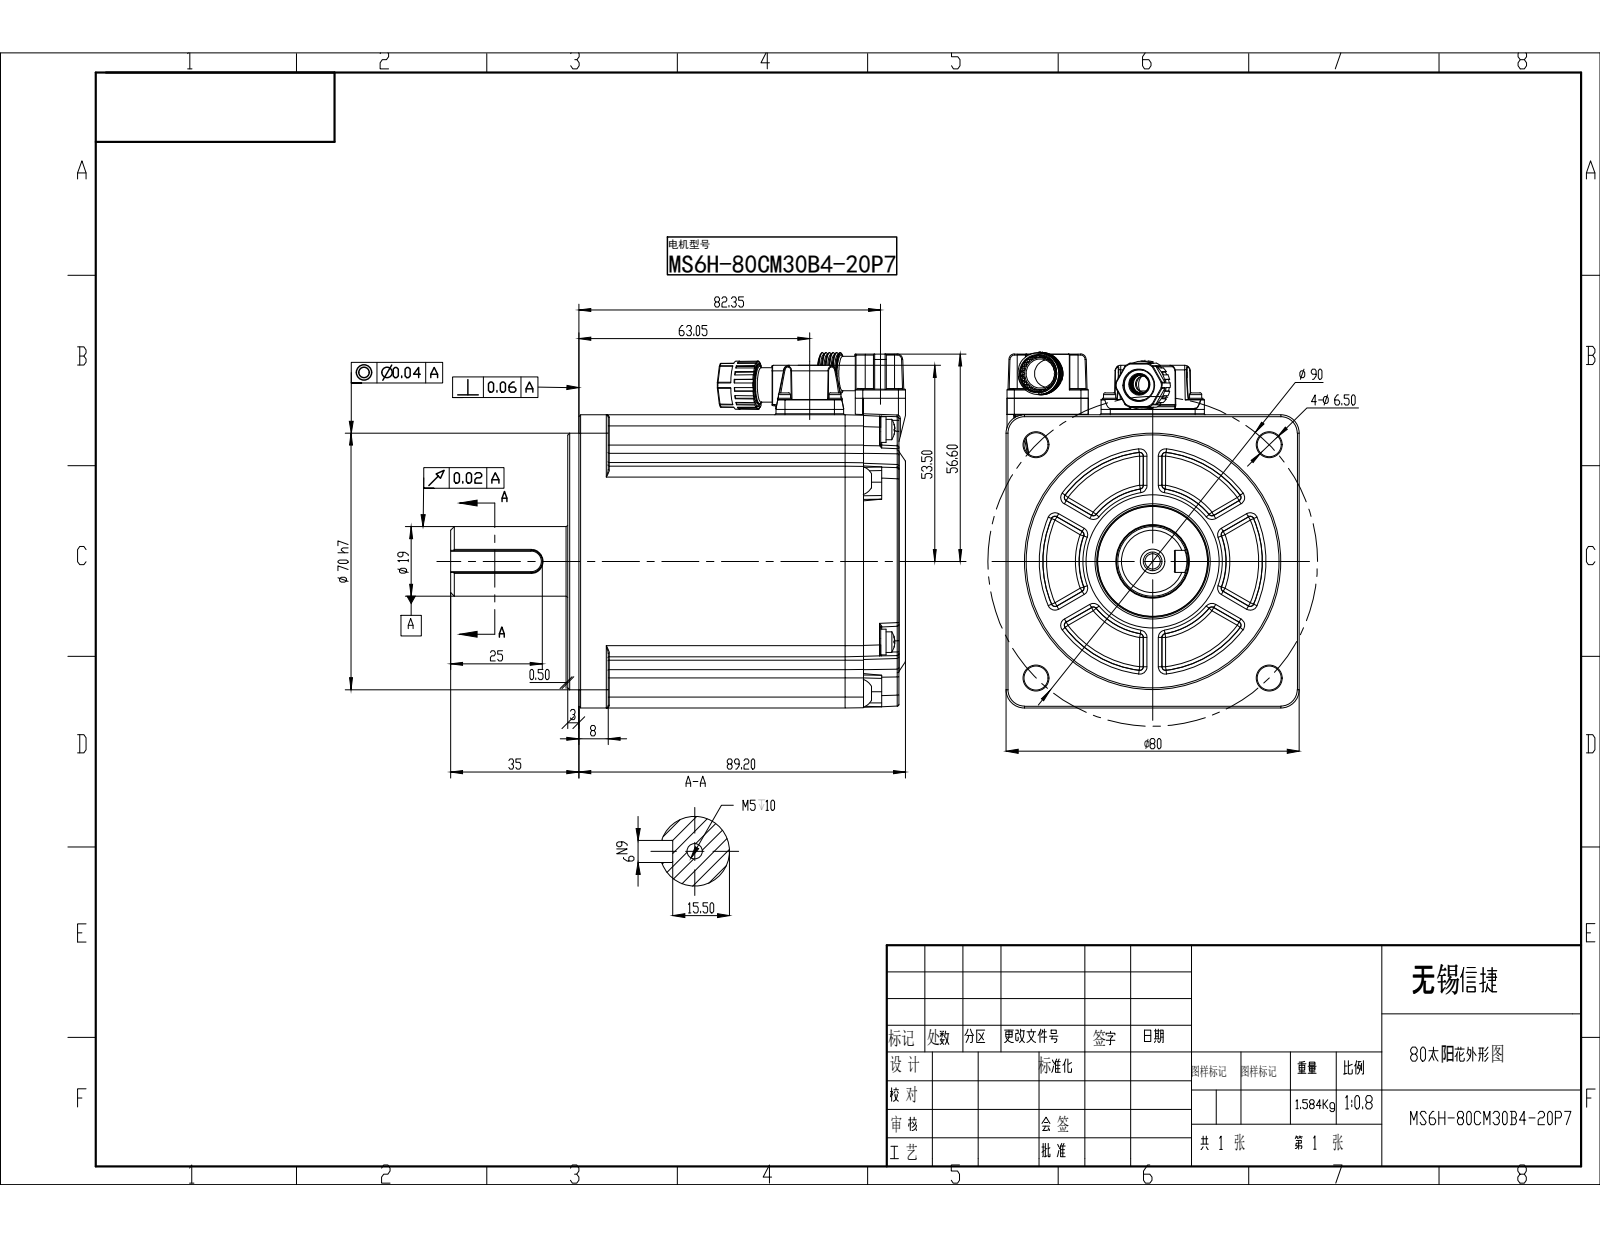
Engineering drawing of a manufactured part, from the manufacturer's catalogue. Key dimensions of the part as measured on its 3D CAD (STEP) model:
Part name (STEP PRODUCT): X2_FF16FF50_X0; X2_87BA4E1D_X0_-L7.0; zhen-SD; stator_1 (+7 more)
STEP written by: SolidWorks 2016 (CONFIG_CONTROL_DESIGN)
Units: millimetres
Bodies: 92 solids, 6307 faces (2332 planar, 2227 cylindrical, 1748 other)
Overall size (bounding box): 124.2 × 96.98 × 80
Volume: 380 526 mm³ · Surface area: 263 987 mm²
Round holes (diameter × count): ⌀1 ×36, ⌀1.6 ×12, ⌀2.2 ×11, ⌀2.5 ×7, ⌀4.5 ×5, ⌀3.3 ×4, ⌀3.5 ×4, ⌀6.5 ×4, ⌀2 ×3, ⌀1.4 ×2, ⌀3.2 ×2, ⌀2.05 ×1
Round bosses / shafts (diameter × count): ⌀4 ×5, ⌀7 ×4, ⌀5.6 ×4, ⌀3.9 ×4, ⌀3.3 ×4, ⌀3 ×4, ⌀2.6 ×4, ⌀1.7 ×4
Partial cylindrical surfaces — rounded edges, fillets, slot ends (radius × count): R0.2 ×282, R0.3 ×252, R0.5 ×200, R0.1 ×132, R0.4 ×102, R0.35 ×50, R1 ×49, R0.25 ×36
Main face-to-face distances: 0.5, 7.6, 80, 3.1, 8.1, 28.06, 28.56, 36.16, 36.66, 14
Hole centre spacings: 27.6, 31.25, 29.59, 41.69, 3.65, 15.64, 14.29, 15.63
